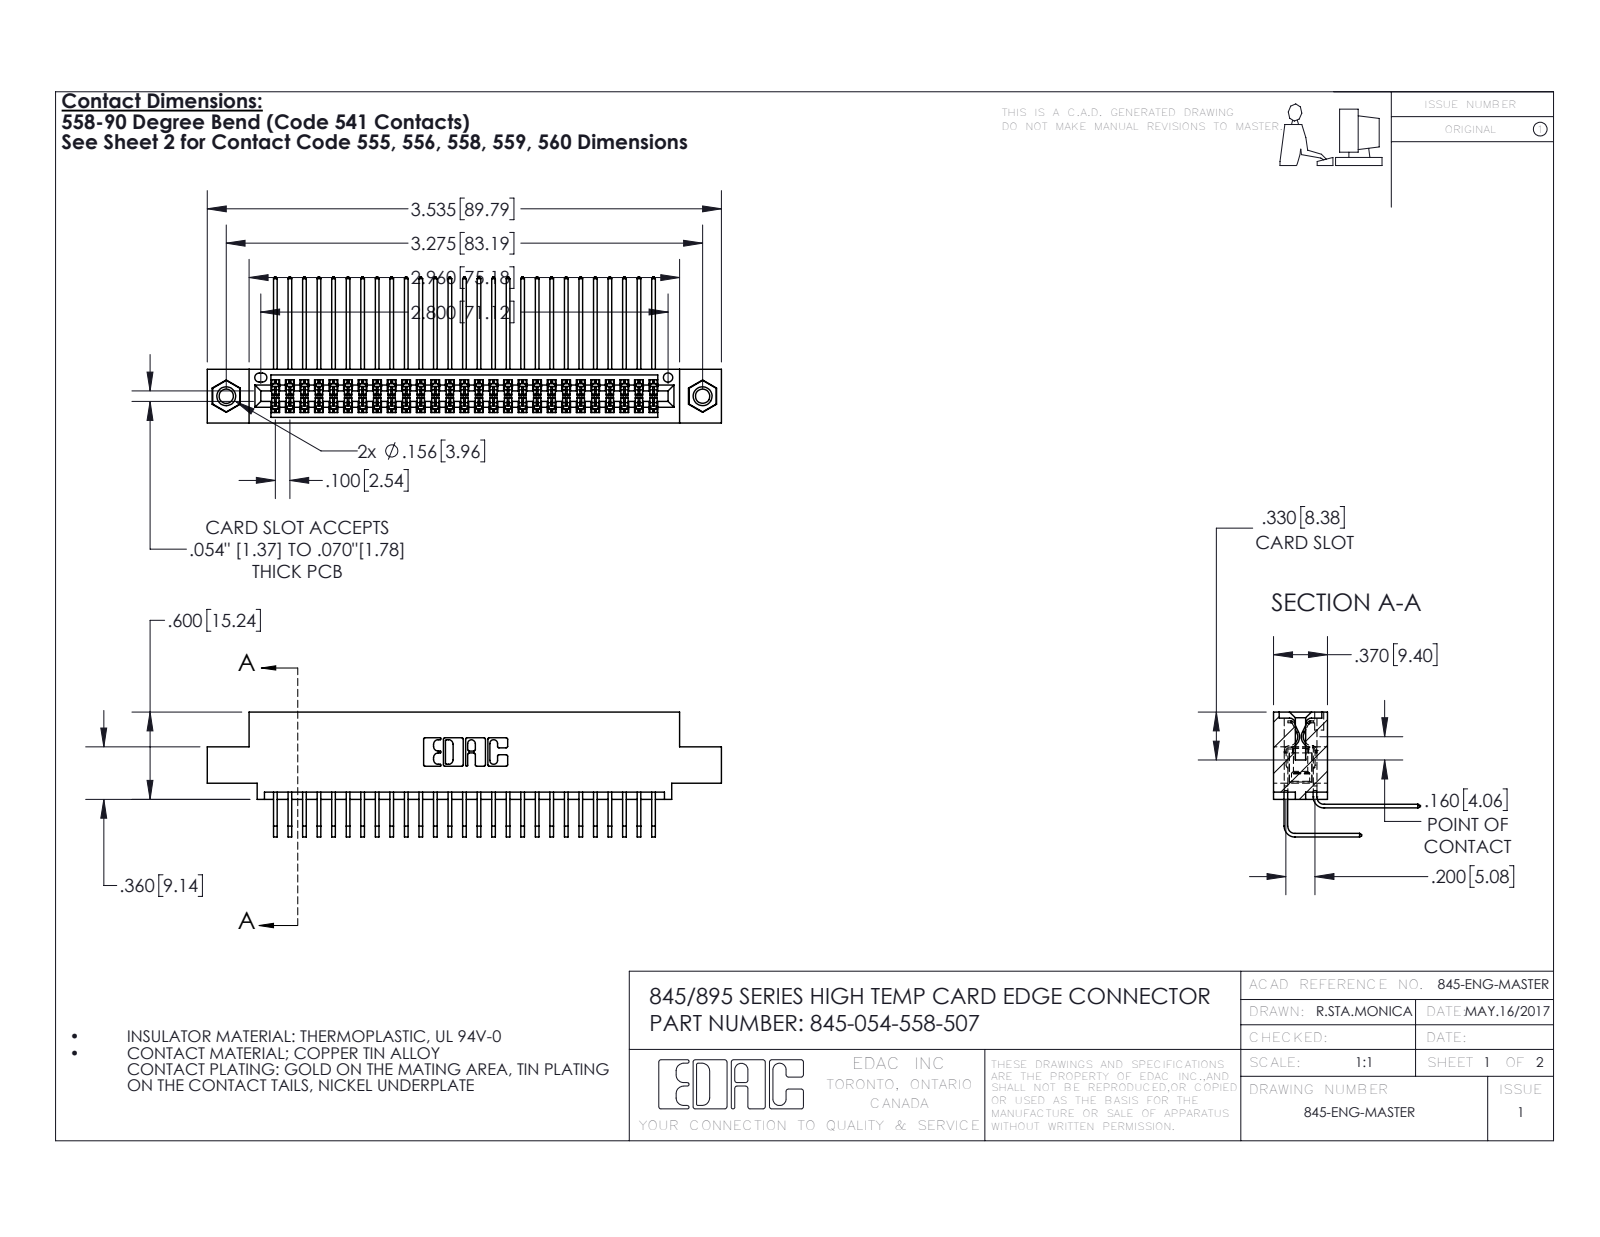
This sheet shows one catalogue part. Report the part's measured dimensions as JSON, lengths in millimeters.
{"part_name": "345 Part_0.110 Offset - 0.156 Dia-TI; 345-250-001_345-250-005-103; 345-054-558-507; 345-292-001_558 559 Tail - 1 (+1 more)", "step_written_by": "SolidWorks 2016 (CONFIG_CONTROL_DESIGN)", "units": "millimeters", "bodies": {"solids": 33, "faces": 1942, "planar": 1334, "cylindrical": 592, "other": 16}, "overall_size": [89.8, 25.5, 21.8], "volume_mm3": 8460, "surface_area_mm2": 11920, "round_holes": [[2.5, 2], [3.2, 2], [4, 2], [1.6, 1]], "round_bosses_or_shafts": [[3.9, 2]], "partial_cylinders_radius": [[0.2, 60], [0.3, 22], [0.2, 6], [0.8, 6], [0.7, 3], [0.4, 2], [0.5, 2], [0.6, 2]], "face_to_face_distances": [1.8, 7.6, 9.4, 5.1, 2.5, 6.9, 0.6, 5.7, 3.8, 1.8], "hole_center_spacings": [6.9, 77.2, 83.2]}
